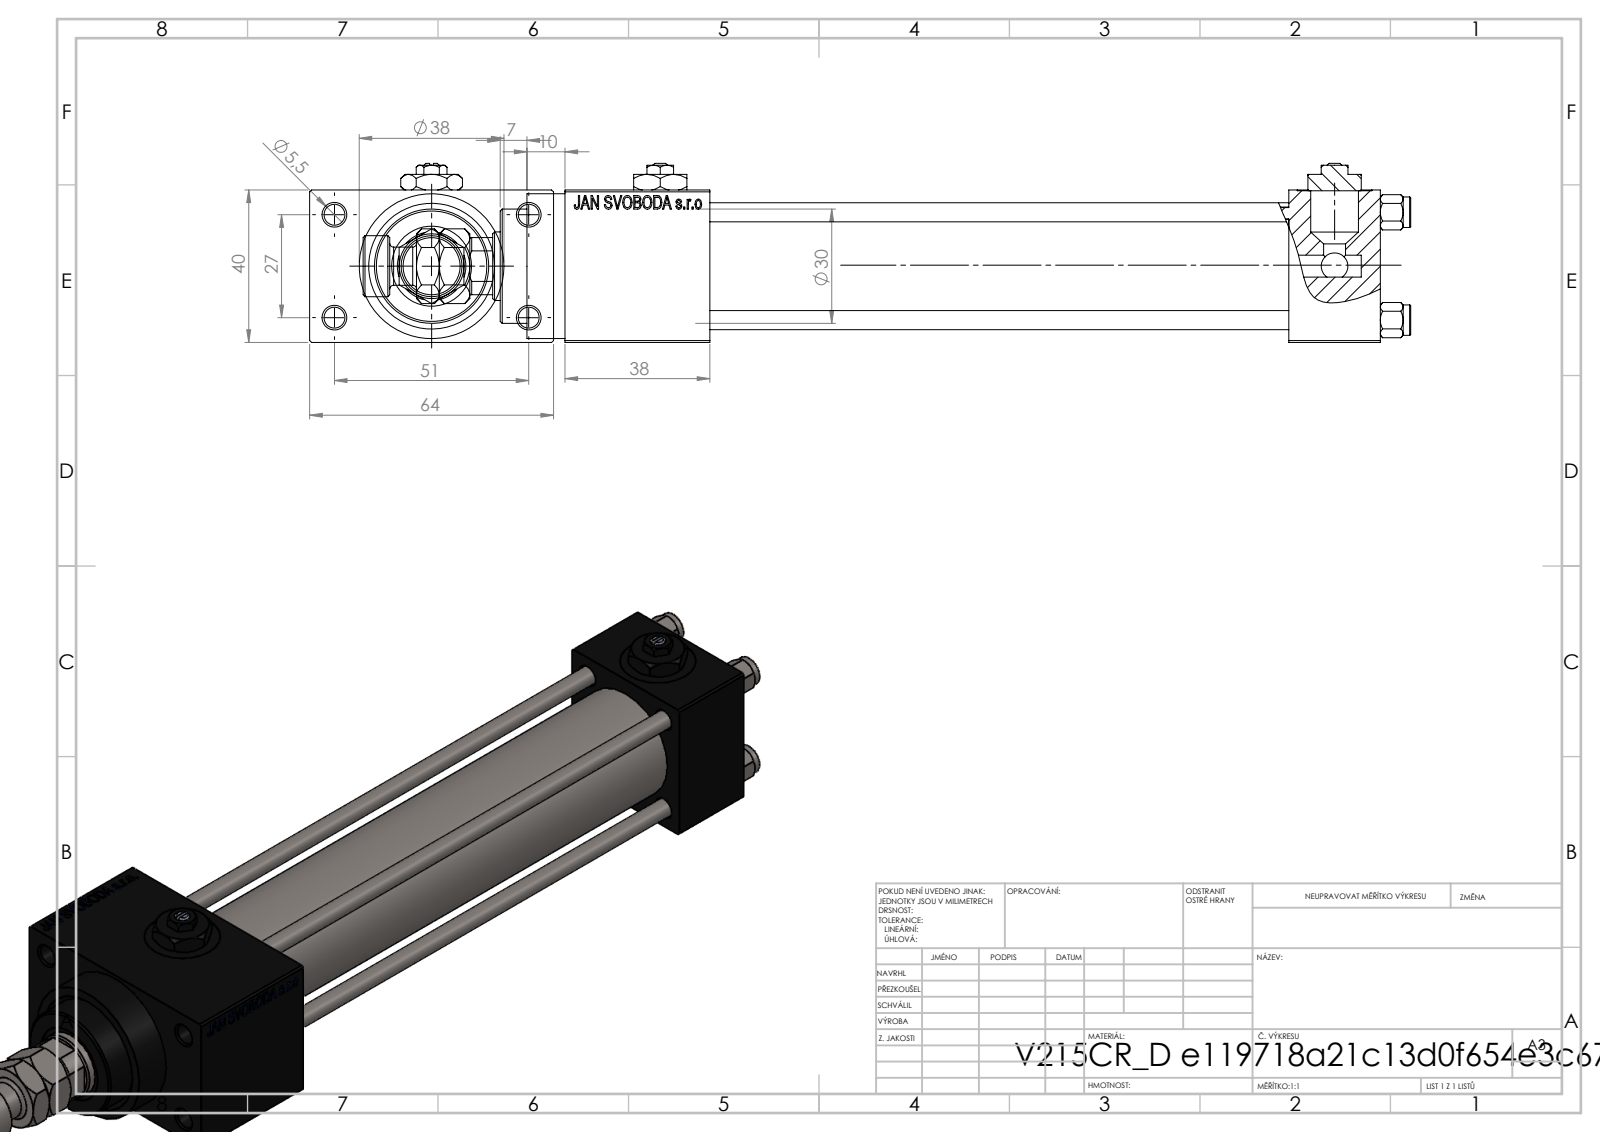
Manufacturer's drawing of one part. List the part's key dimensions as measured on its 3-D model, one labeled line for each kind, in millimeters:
Part name (STEP PRODUCT): V215CR_D_Body; V215CR_D_TYCINKA; Zatka_pro_OIL_PORT; MFA (+3 more)
STEP written by: SolidWorks 2019 (CONFIG_CONTROL_DESIGN)
Units: millimetres
Bodies: 14 solids, 1252 faces (557 planar, 101 cylindrical, 594 other)
Overall size (bounding box): 275 × 64 × 47
Volume: 246 199 mm³ · Surface area: 99 348 mm²
Round holes (diameter × count): ⌀20 ×5, ⌀5 ×4, ⌀5.5 ×4, ⌀13.16 ×4, ⌀7 ×3, ⌀8.5 ×1, ⌀18 ×1, ⌀21 ×1, ⌀25 ×1, ⌀30 ×1
Round bosses / shafts (diameter × count): ⌀8 ×4, ⌀38 ×1, ⌀31 ×1, ⌀16 ×1, ⌀10 ×1
Partial cylindrical surfaces — rounded edges, fillets, slot ends (radius × count): R8.5 ×1
Main face-to-face distances: 40, 12, 152, 24, 176, 52, 38, 190, 214, 64
Hole centre spacings: 11.37, 20.01, 28.3, 28.85, 29.89, 39.66, 48.34, 27
